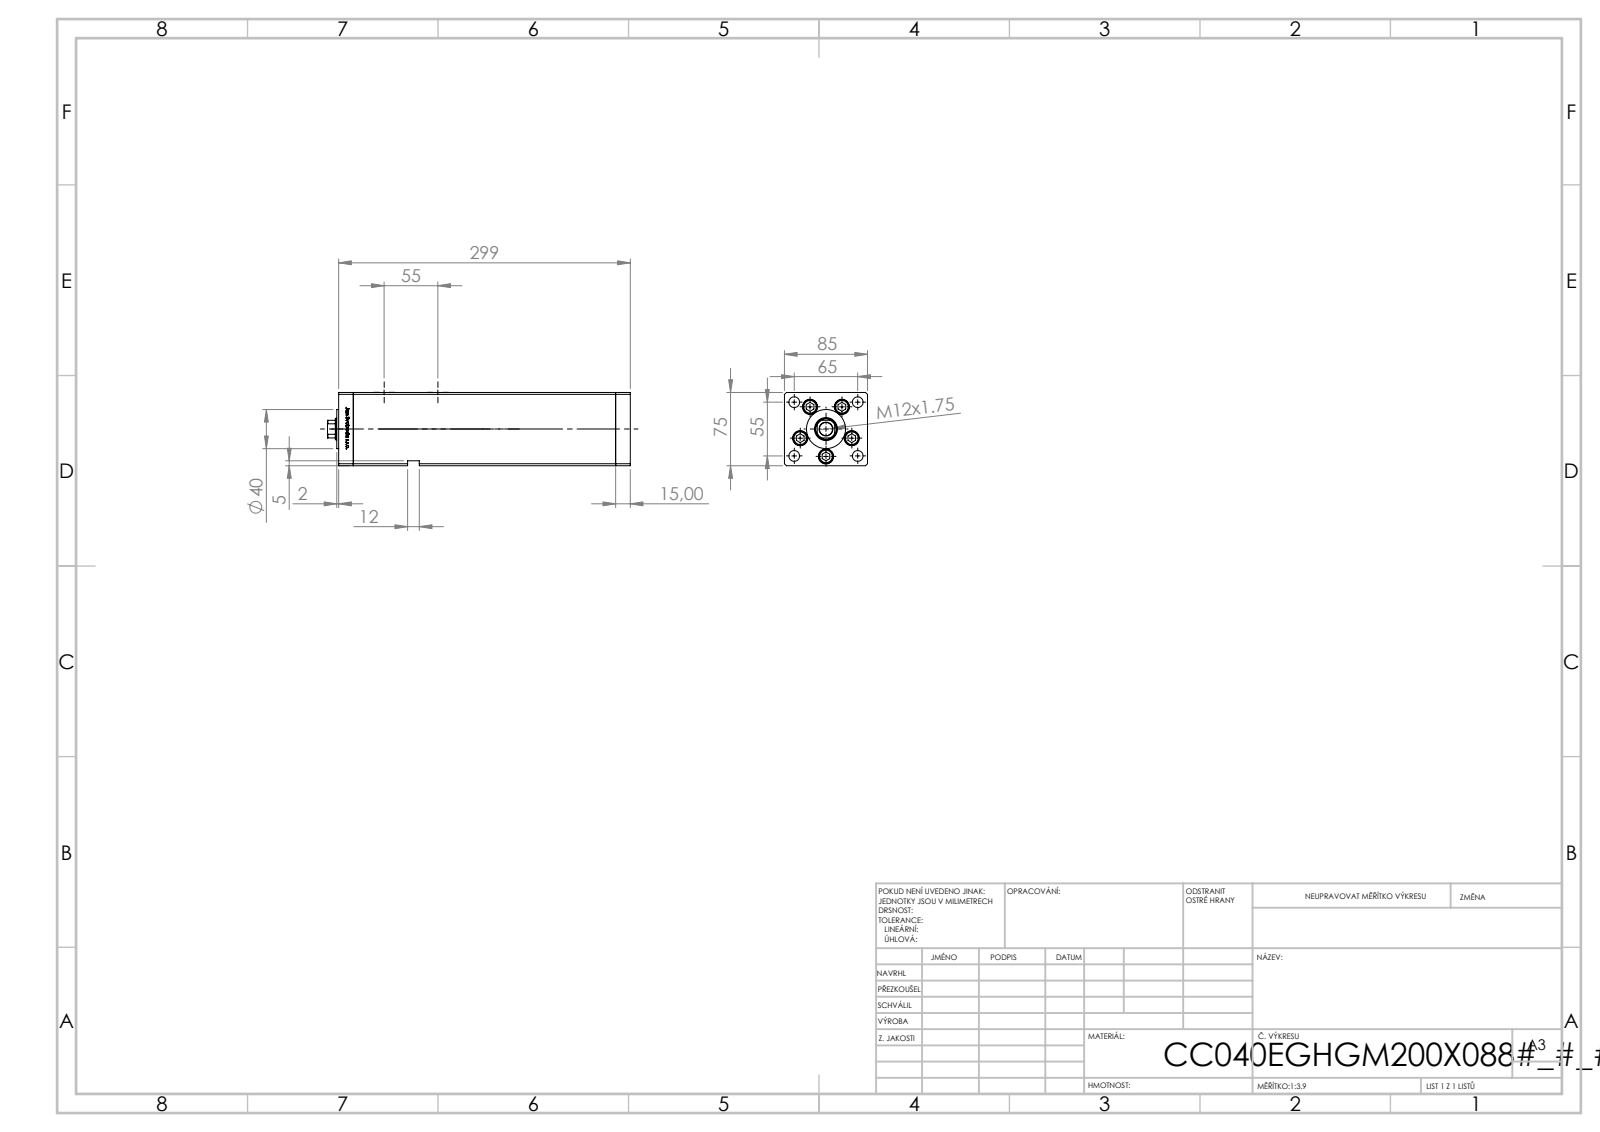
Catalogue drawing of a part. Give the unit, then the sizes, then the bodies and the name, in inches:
Units: inches
Overall size (bounding box): 12.205 × 3.346 × 2.953
Round holes (diameter × count): ⌀0.433 ×9, ⌀0.61 ×5, ⌀0.413 ×4, ⌀0.65 ×4, ⌀0.079 ×2, ⌀0.518 ×2, ⌀0.531 ×1, ⌀0.866 ×1, ⌀0.925 ×1
Round bosses / shafts (diameter × count): ⌀0.571 ×5, ⌀0.315 ×5, ⌀1.575 ×1
Partial cylindrical surfaces — rounded edges, fillets, slot ends (radius × count): R0.037 ×2, R0.413 ×1
Main face-to-face distances: 3.346, 2.953, 0.591, 10.571, 11.161, 0.413, 11.752, 2.539, 2.697, 1.23
Hole centre spacings: 1.102, 1.676, 2.165, 2.559, 3.352, 0.664, 0.755, 1.273
Volume: 98 in³ · Surface area: 366.2 in²
Bodies: 14 solids, 1212 faces (473 planar, 165 cylindrical, 574 other)
Part name (STEP PRODUCT): V220C_VC_E; ALLEN BOLT; V220C_E MIDDLE; V220C_FRONT_E (+1 more)
STEP written by: SolidWorks 2019 (CONFIG_CONTROL_DESIGN)
